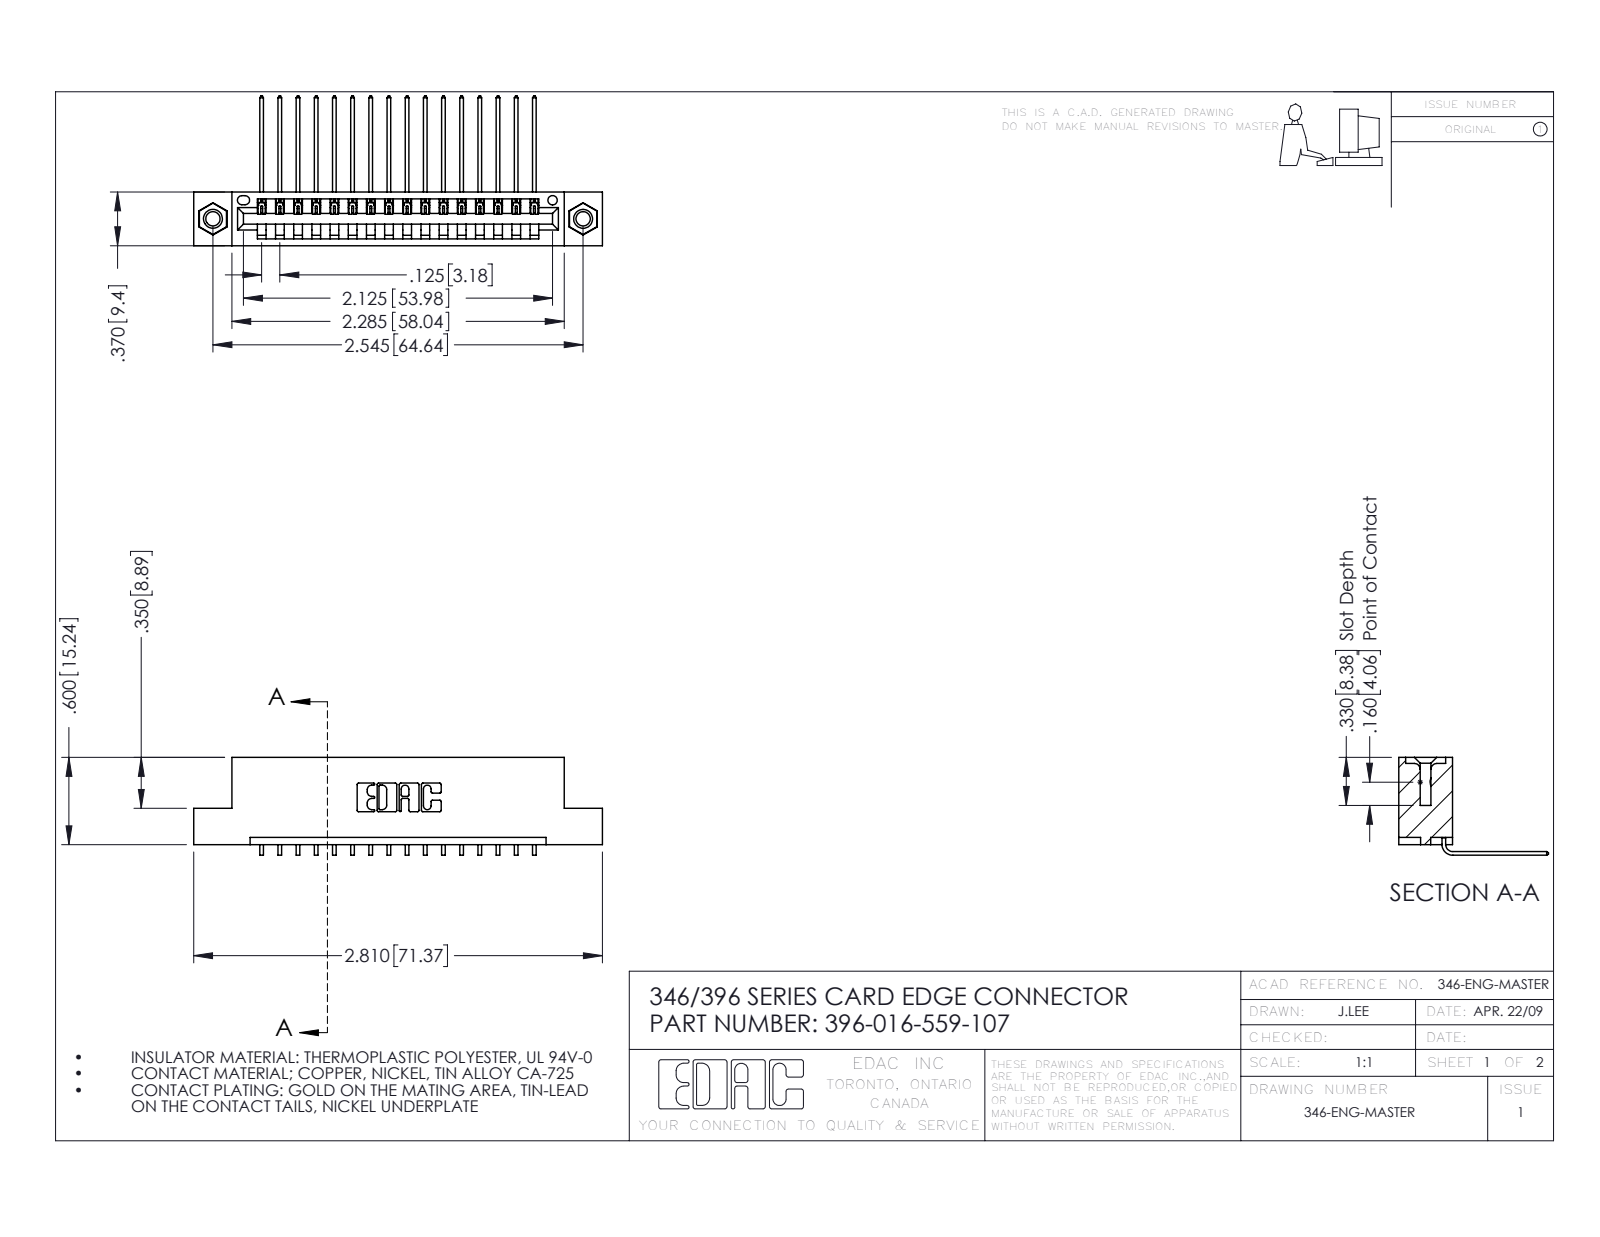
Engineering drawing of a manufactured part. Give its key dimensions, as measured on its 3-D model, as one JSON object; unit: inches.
{"part_name": "396-016-559-107; 345-250-001_345-250-005-103; 346 Part_Flush Mounting Lugs - 0.156 Dia-TI; 345-292-001_558 559 Tail - 1", "step_written_by": "SolidWorks 2016 (CONFIG_CONTROL_DESIGN)", "units": "inches", "bodies": {"solids": 19, "faces": 1142, "planar": 780, "cylindrical": 346, "other": 16}, "overall_size": [2.81, 1.03, 0.673], "volume_in3": 0.408, "surface_area_in2": 13.08, "round_holes": [[0.098, 2], [0.125, 2], [0.156, 2], [0.064, 1]], "round_bosses_or_shafts": [[0.155, 2]], "partial_cylinders_radius": [[0.006, 32], [0.01, 22], [0.007, 6], [0.031, 6], [0.026, 3], [0.031, 2], [0.04, 2], [0.014, 1]], "face_to_face_distances": [0.048, 0.322, 0.37, 0.25, 0.072, 0.025, 0.298, 0.148, 0.222, 0.1], "hole_center_spacings": [0.246, 2.338, 2.545]}
